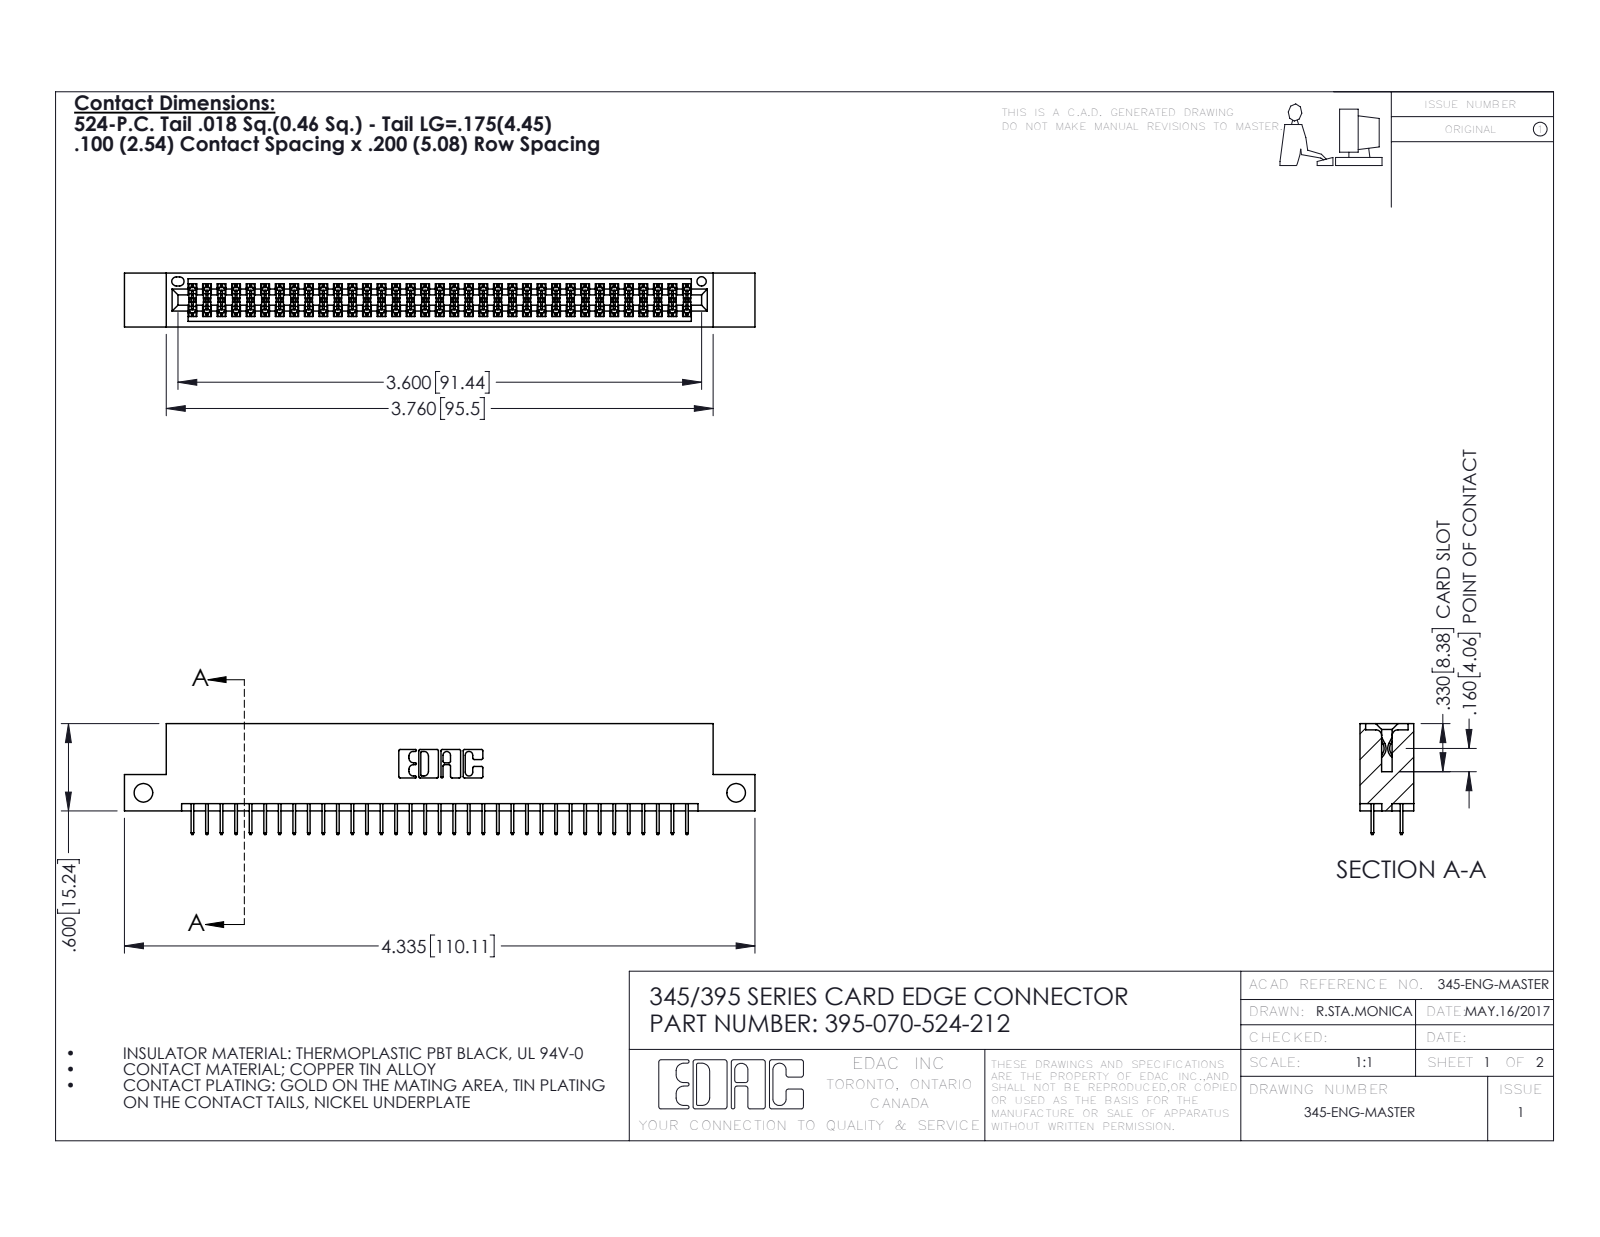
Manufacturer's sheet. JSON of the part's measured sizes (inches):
{"part_name": "395-070-524-212; 345-292-001_345-293-124; 345 Part_Flush Mounting Lugs - Side Mount", "step_written_by": "SolidWorks 2016 (CONFIG_CONTROL_DESIGN)", "units": "inches", "bodies": {"solids": 71, "faces": 3906, "planar": 2810, "cylindrical": 1096, "other": 0}, "overall_size": [4.335, 0.762, 0.37], "volume_in3": 0.637, "surface_area_in2": 23.06, "round_holes": [[0.128, 2], [0.064, 1]], "partial_cylinders_radius": [[0.006, 105], [0.01, 22], [0.007, 6], [0.031, 6], [0.026, 3], [0.014, 2], [0.019, 2], [0.022, 2]], "face_to_face_distances": [0.298, 0.072, 0.2, 0.37, 0.098, 0.272, 0.025, 0.225, 0.072, 0.175], "hole_center_spacings": [4.075]}
